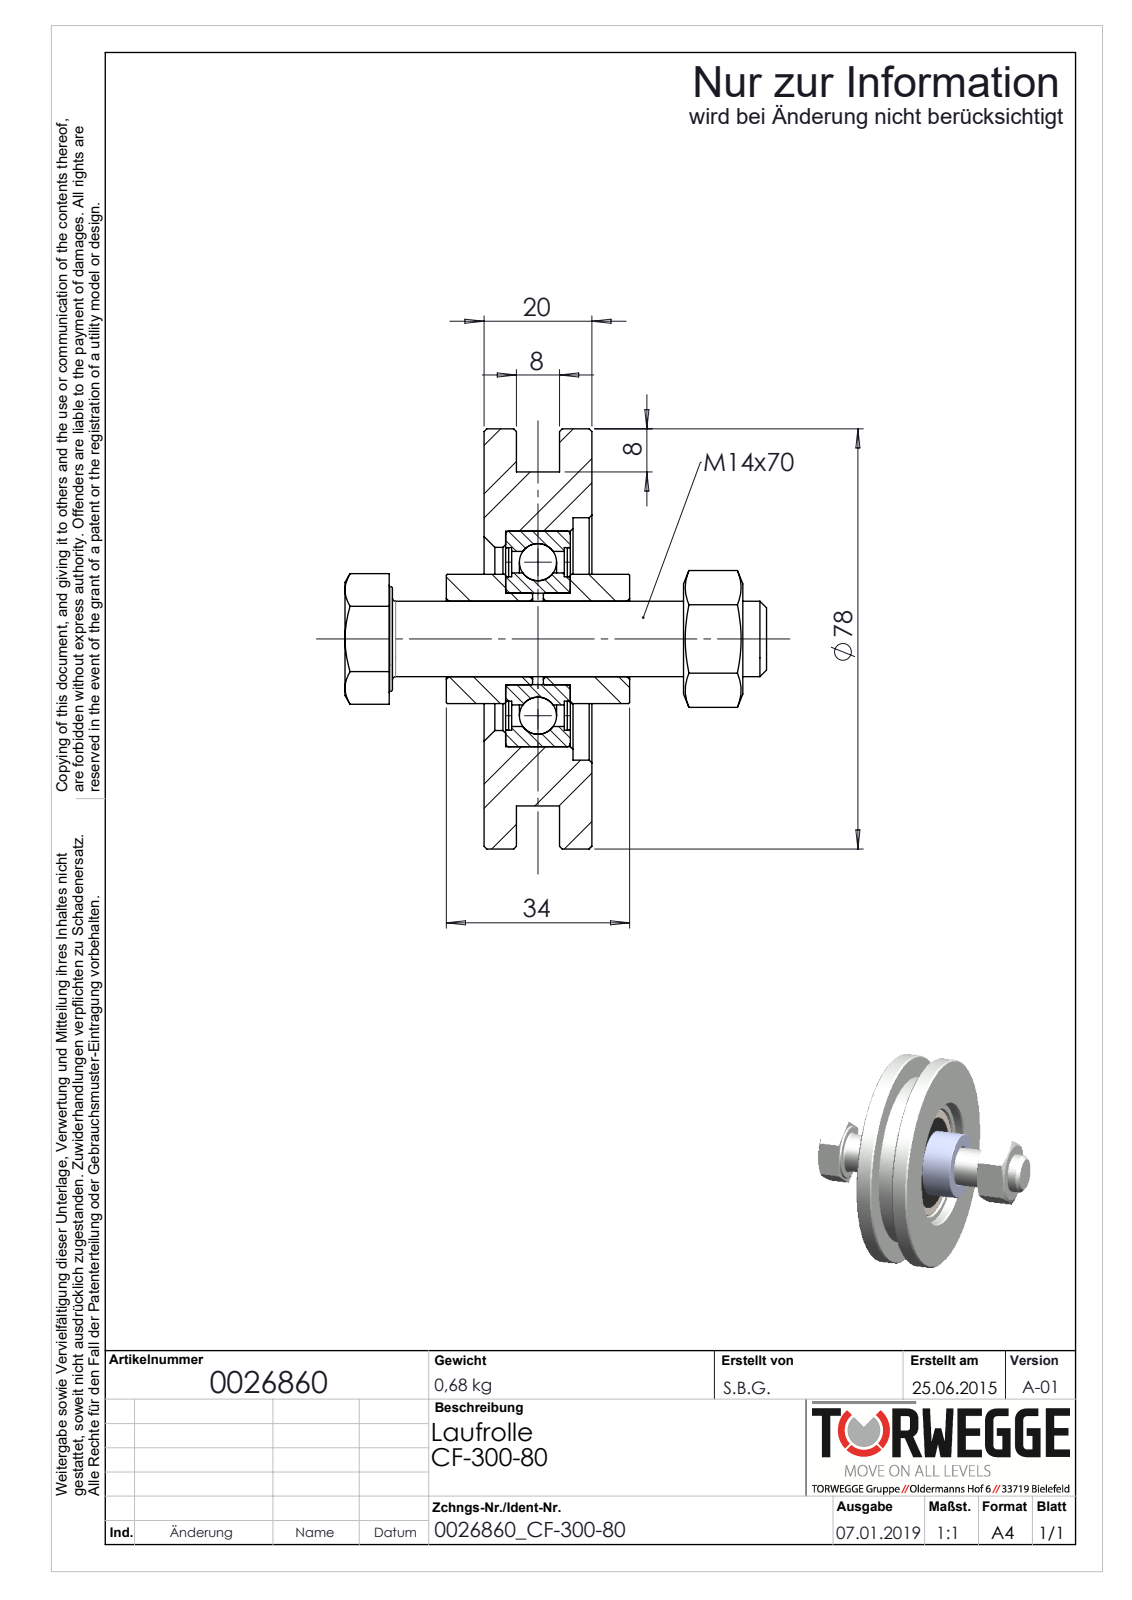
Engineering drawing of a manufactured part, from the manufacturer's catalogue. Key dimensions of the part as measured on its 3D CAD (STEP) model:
Part name (STEP PRODUCT): 0026860_CF-300-80_(A-01)
STEP written by: SolidWorks 2018 (AUTOMOTIVE_DESIGN)
Units: millimetres
Bodies: 10 solids, 182 faces (42 planar, 56 cylindrical, 84 other)
Overall size (bounding box): 78.2 × 78 × 78
Volume: 91 118 mm³ · Surface area: 38 300 mm²
Round holes (diameter × count): ⌀12 ×1, ⌀14 ×1, ⌀23.1 ×1, ⌀32.5 ×1, ⌀33.91 ×1, ⌀34 ×1, ⌀40 ×1, ⌀45 ×1
Round bosses / shafts (diameter × count): ⌀78 ×1, ⌀62 ×1, ⌀24.5 ×1, ⌀24 ×1, ⌀17 ×1
Main face-to-face distances: 6, 14, 20, 10, 16, 4, 2, 8, 0.56, 12
